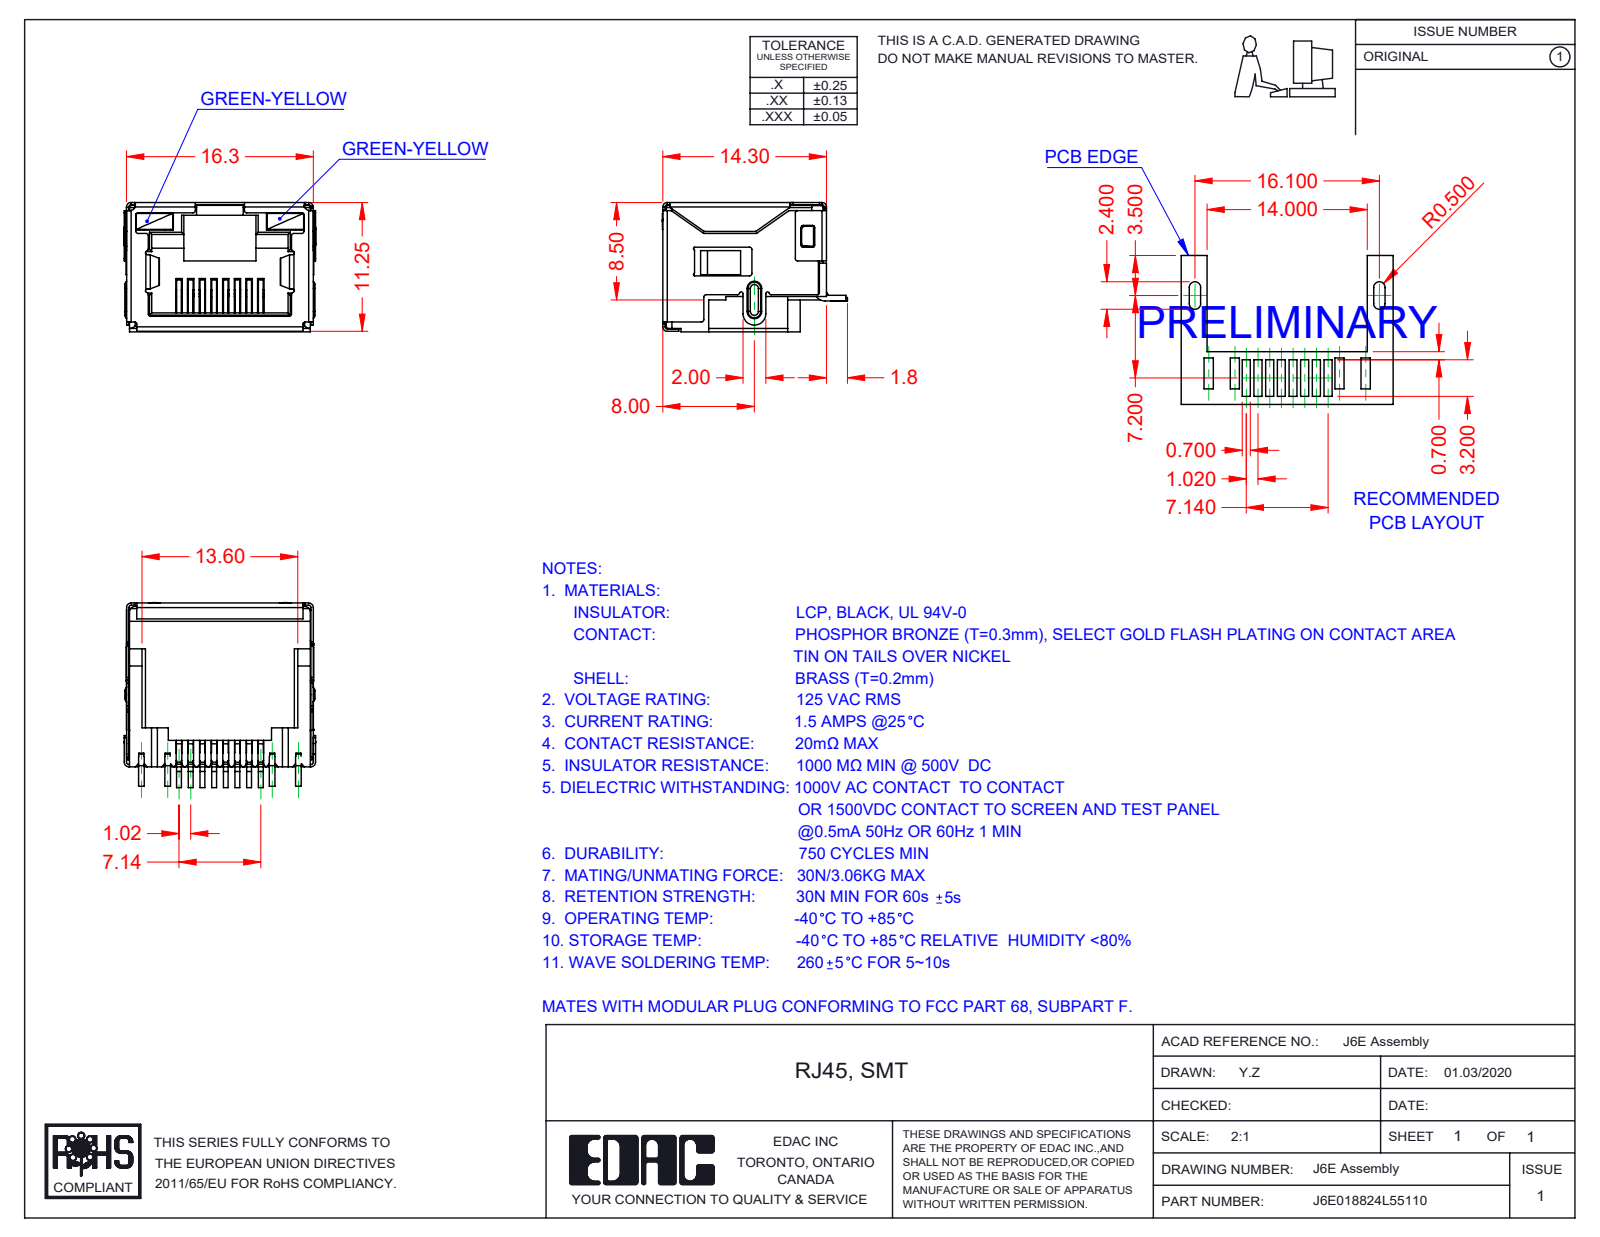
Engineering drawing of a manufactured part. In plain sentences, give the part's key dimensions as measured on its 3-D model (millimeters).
The part is named "J6E018824L55110; 6E Insulator_LED; 6E LED LH_5-Green-Yellow; 6E Contacts (+2 more)". Its 3-D file was written by "SolidWorks 2016 (CONFIG_CONTROL_DESIGN)". It is 12 solids with 1500 faces: 1099 planar, 351 cylindrical and 50 other. Overall it measures 16.75 by 16.15 by 11.3 millimeters. Its volume is 1 109 cubic millimeters and its surface area 4 045 square millimeters. Partial cylindrical surfaces (rounded edges, fillets, slot ends): 82 of radius 0.2, 17 of radius 0.25, 13 of radius 0.4, 13 of radius 0.5, 10 of radius 0.1, 7 of radius 0.15, 4 of radius 0.3, 3 of radius 1. The main face-to-face distances are 11.05, 16.05, 16.1, 15.85, 11.1, 11.3, 2.4, 0.7, 9.85, 0.49.
